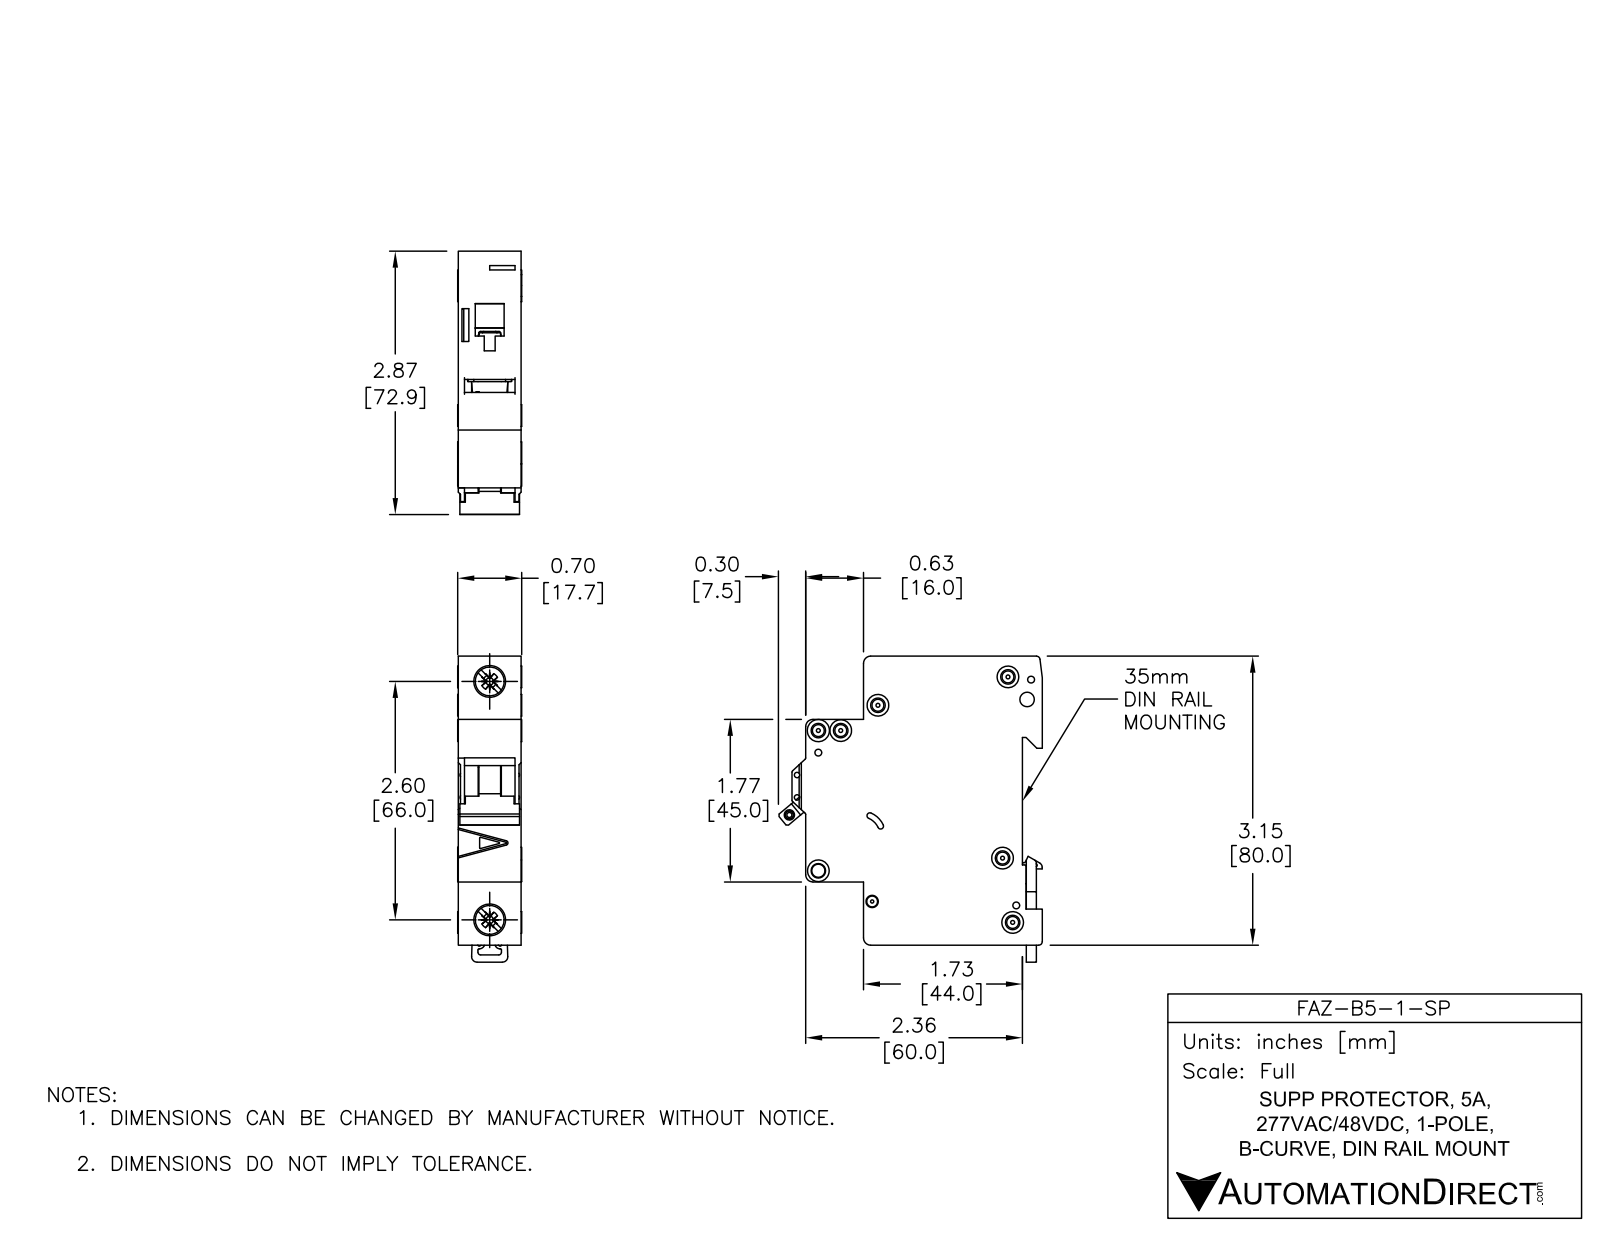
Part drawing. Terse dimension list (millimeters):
name: FAZ-B5-1-SP
written by: SolidWorks 2014 (AUTOMOTIVE_DESIGN)
unit: mm
bodies: 5 solids, 558 faces (235 planar, 202 cylindrical, 121 other)
size: 84.78 × 73.04 × 17.7
volume: 74 935 mm³; area: 19 545 mm²
holes: 6× ⌀3.6, 3× ⌀1.9, 2× ⌀1.09, 2× ⌀1.5, 2× ⌀4, 2× ⌀7.15, 1× ⌀2.15, 1× ⌀2.2, 1× ⌀2.55, 1× ⌀3.3, 1× ⌀3.4
bosses: 4× ⌀6, 2× ⌀8.2, 1× ⌀2.5
rounds: 30× R0.25, 13× R0.5, 8× R2, 5× R0.2, 4× R1, 2× R0.8, 2× R3, 1× R1.5
face distances: 17.5, 79.48, 5.5, 49.5, 44, 65.5, 60, 16, 1.75, 15.75
hole spacings: 6.2, 13.64, 4.81, 5.19, 5.61, 6.1, 6.44, 8.19
